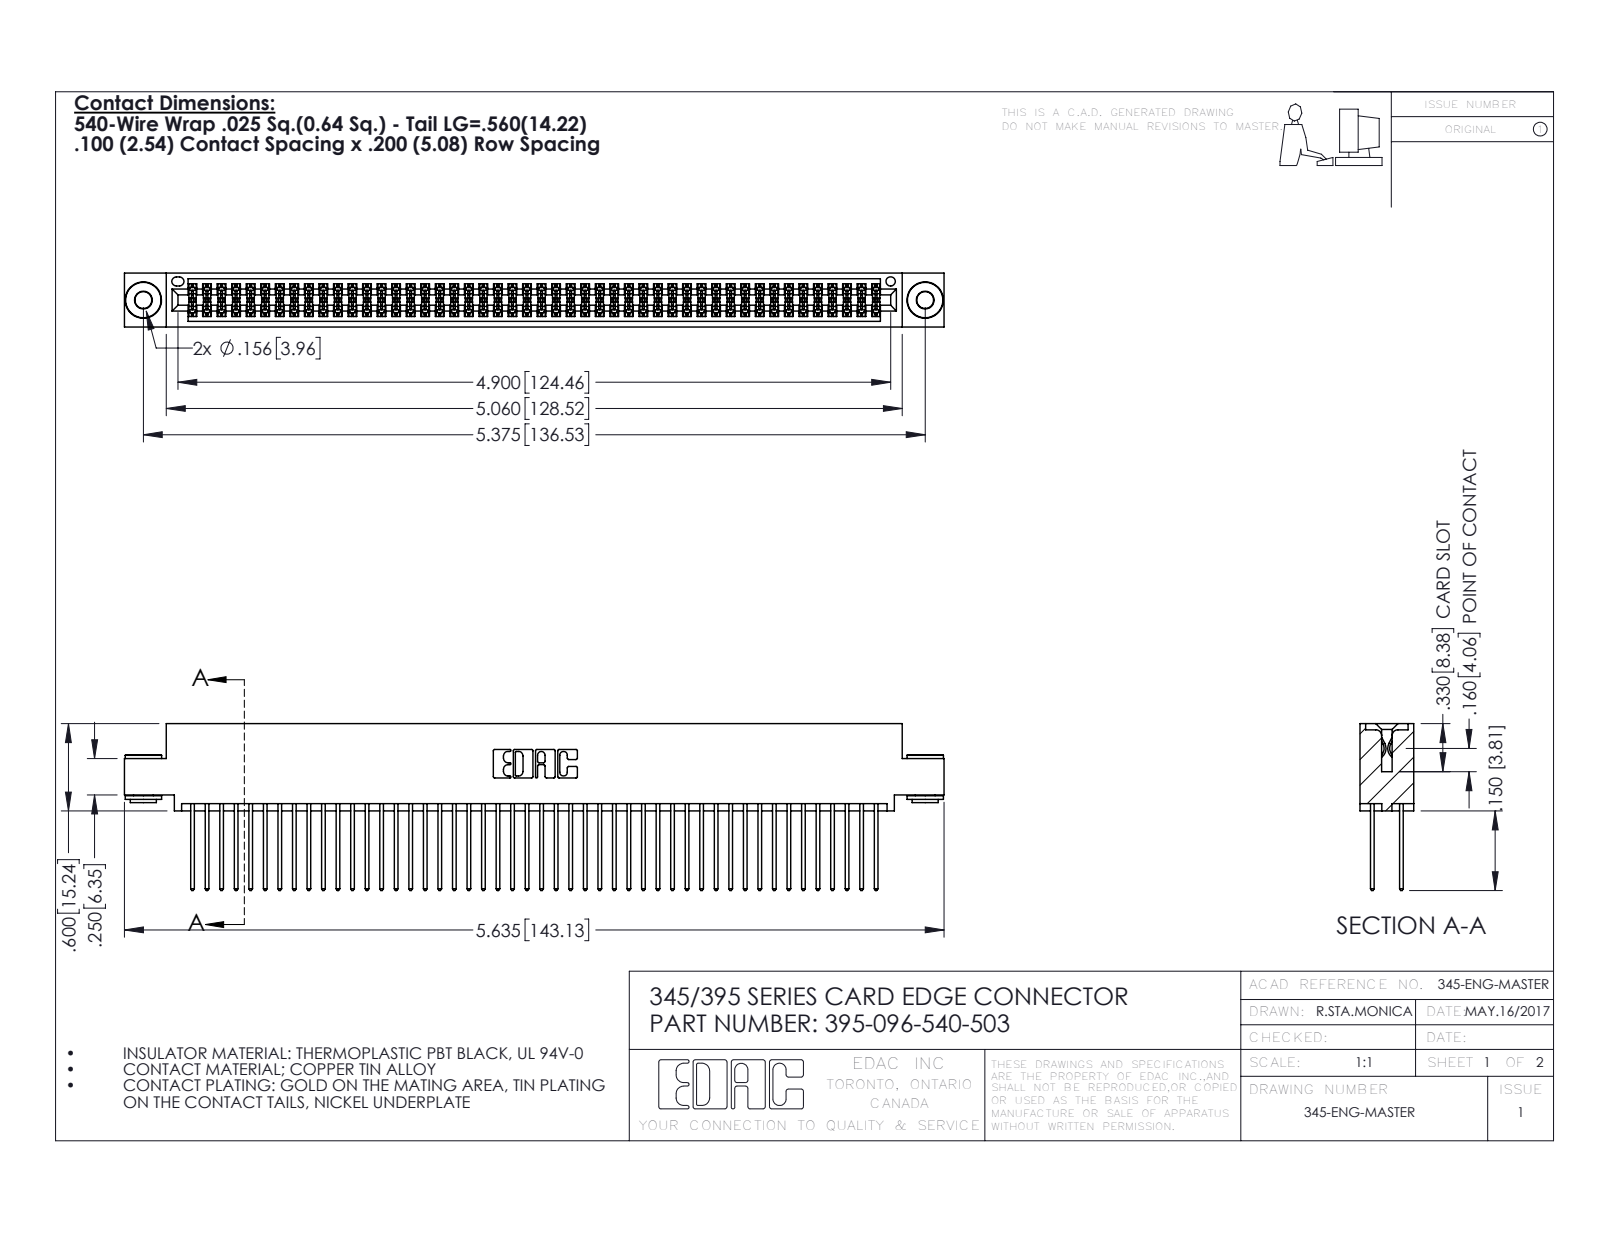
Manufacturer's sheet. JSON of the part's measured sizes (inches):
{"part_name": "395-096-540-503; 345 Part_0.110 Offset - 0.156 Dia-TH; 345-250-002_345-250-002-102; 345-292-001_345-293-140", "step_written_by": "SolidWorks 2016 (CONFIG_CONTROL_DESIGN)", "units": "inches", "bodies": {"solids": 99, "faces": 4968, "planar": 3262, "cylindrical": 1698, "other": 8}, "overall_size": [5.635, 1.147, 0.37], "volume_in3": 0.871, "surface_area_in2": 35.95, "round_holes": [[0.116, 2], [0.156, 2], [0.064, 1]], "round_bosses_or_shafts": [[0.25, 2], [0.18, 2], [0.136, 2]], "partial_cylinders_radius": [[0.006, 144], [0.01, 96], [0.01, 22], [0.007, 6], [0.031, 6], [0.026, 3], [0.014, 2], [0.019, 2]], "face_to_face_distances": [0.072, 0.298, 0.2, 0.025, 0.098, 0.272, 0.37, 0.225, 0.175, 0.149], "hole_center_spacings": [0.27, 5.139, 5.375]}
